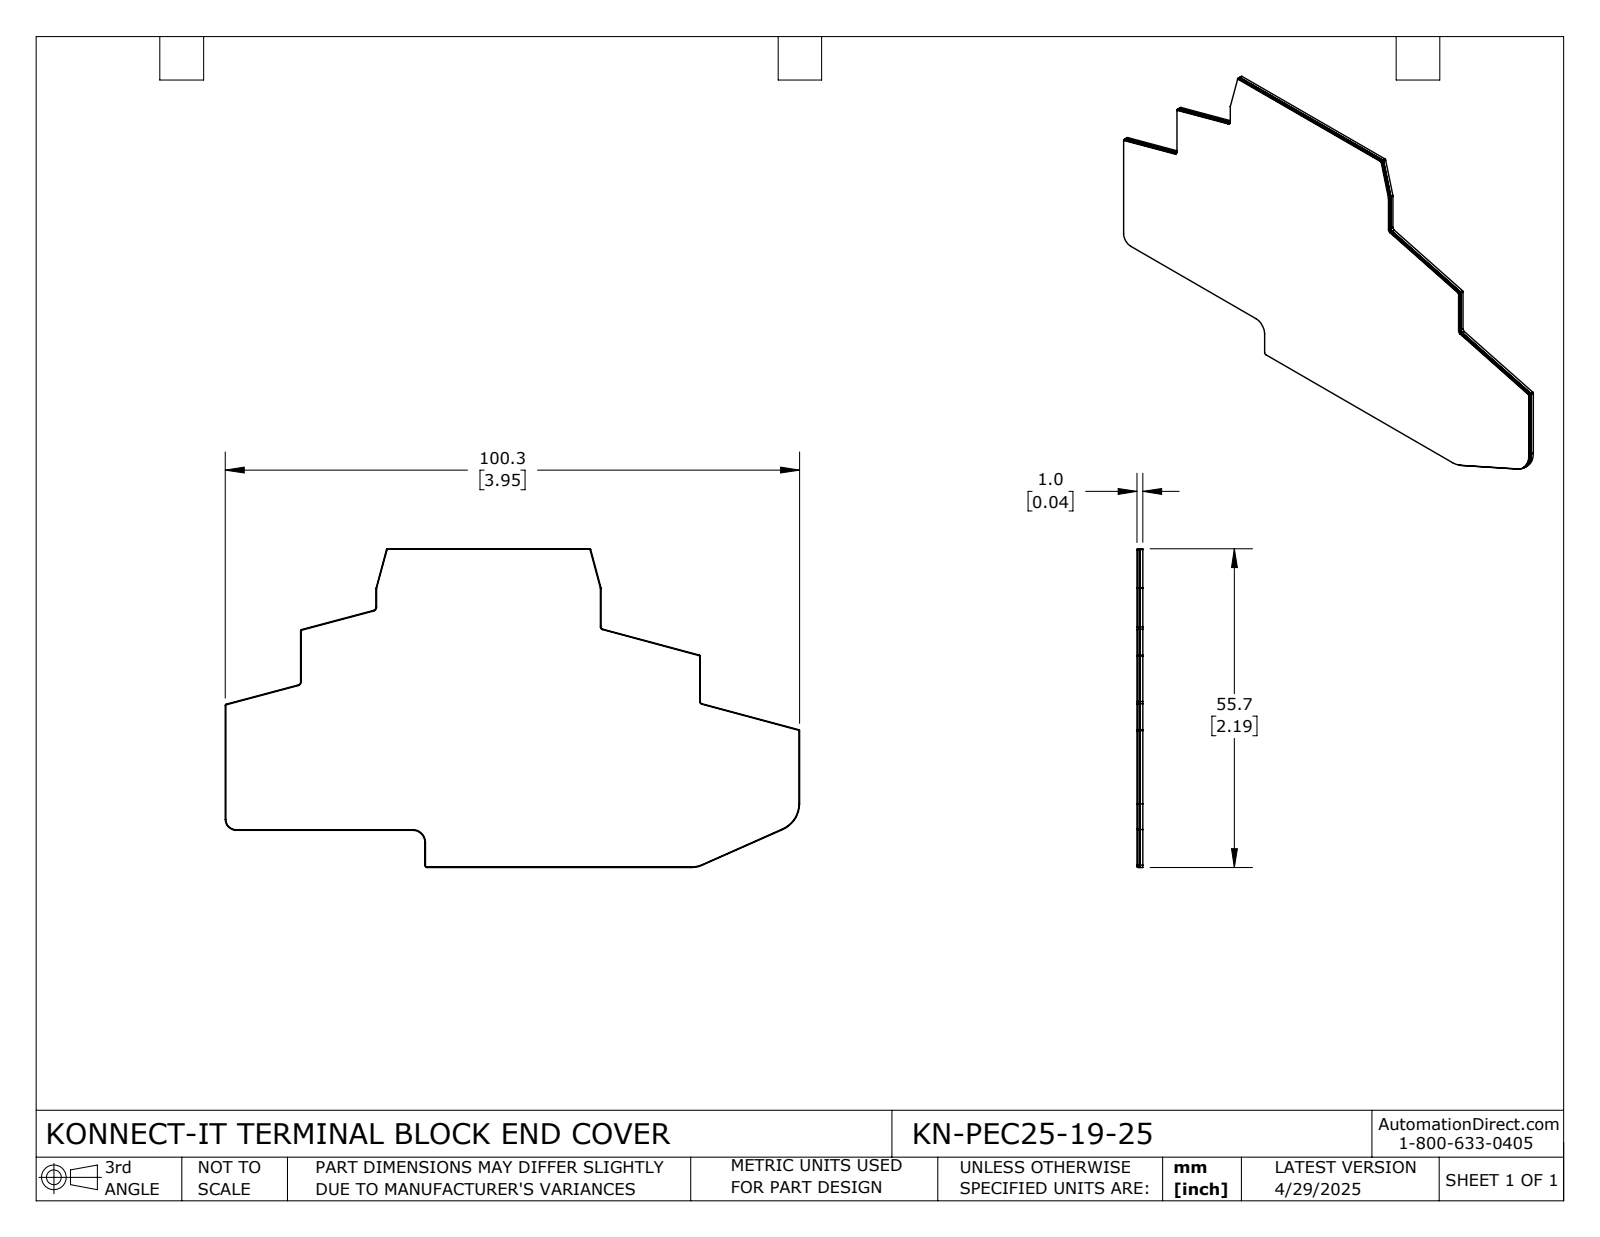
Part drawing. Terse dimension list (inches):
name: KN-PEC25-19-25
written by: SolidWorks 2024 (CONFIG_CONTROL_DESIGN)
unit: in
bodies: 2 solids, 107 faces (56 planar, 51 cylindrical, 0 other)
size: 3.948 × 2.191 × 0.039
volume: 0.243 in³; area: 25.12 in²
rounds: 8× R0.004, 8× R0.008, 3× R0.016, 2× R0.02, 2× R0.024, 2× R0.028, 2× R0.189, 2× R0.193
face distances: 0.02, 0.039, 0.257, 2.191, 0.033, 0.014, 1.935, 0.319, 0.361, 2.187
